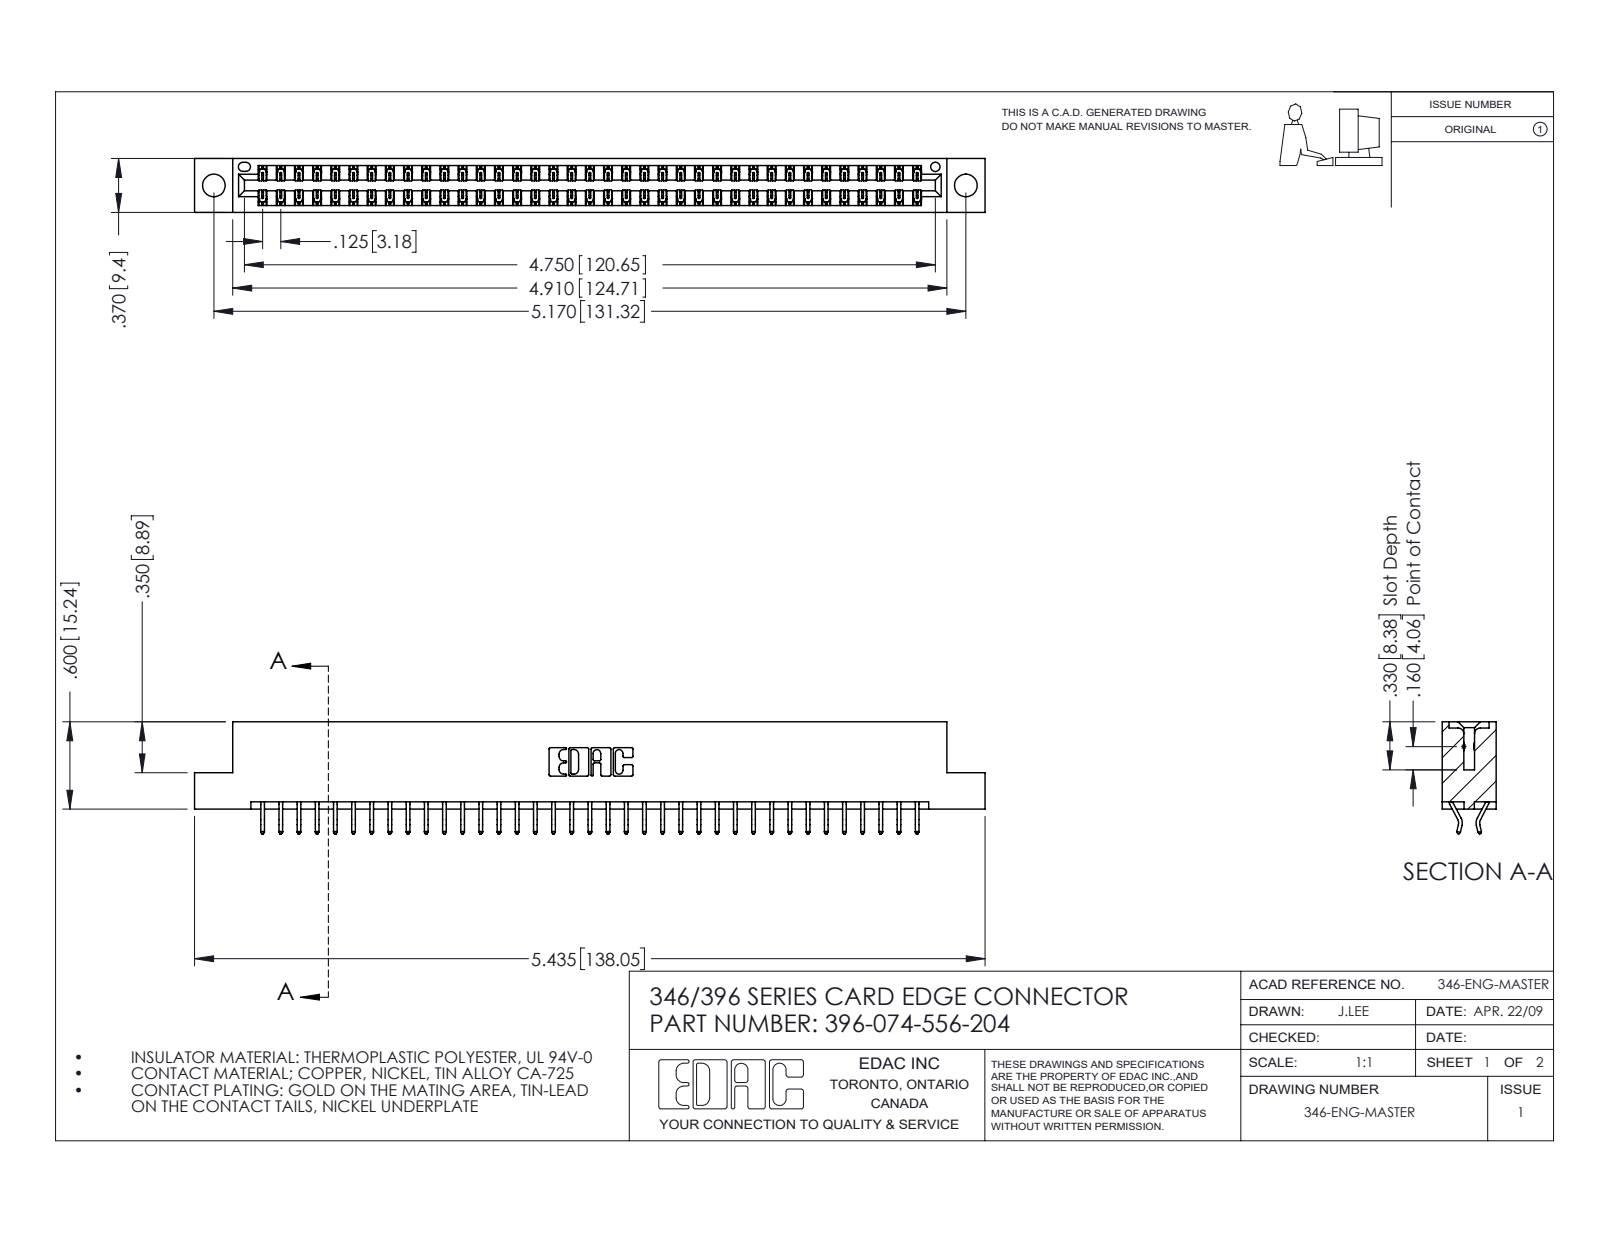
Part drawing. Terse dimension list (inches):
name: 396-074-556-204; 345-292-001_556 Tail; 346 Part_Flush Mounting Lugs - 0.156 Dia-TH
written by: SolidWorks 2016 (CONFIG_CONTROL_DESIGN)
unit: in
bodies: 75 solids, 4414 faces (2962 planar, 1452 cylindrical, 0 other)
size: 5.435 × 0.77 × 0.37
volume: 0.814 in³; area: 27.89 in²
holes: 2× ⌀0.156, 1× ⌀0.064
rounds: 111× R0.006, 22× R0.01, 6× R0.007, 6× R0.031, 3× R0.026, 2× R0.01, 2× R0.014, 2× R0.022
face distances: 0.048, 0.322, 0.37, 0.25, 0.025, 0.072, 0.298, 0.275, 0.148, 0.222
hole spacings: 0.246, 4.961, 5.17
